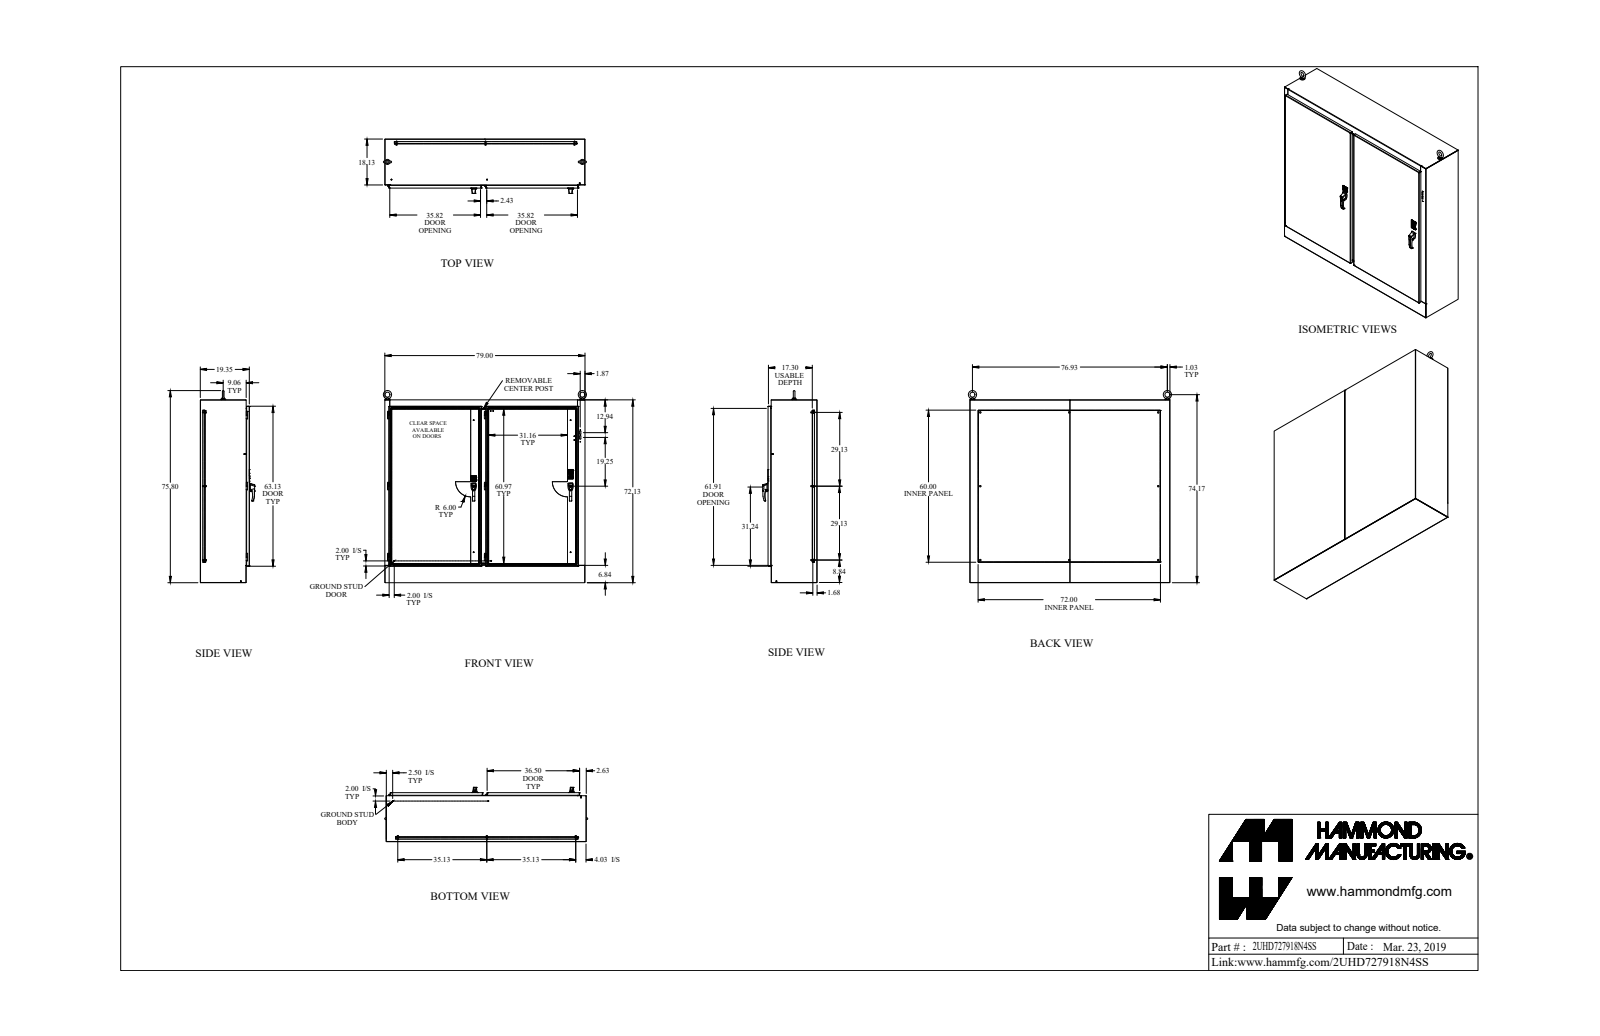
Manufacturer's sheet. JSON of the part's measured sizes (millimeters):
{"part_name": "2UHD727918N4SS", "step_written_by": "SolidWorks 2018 (AUTOMOTIVE_DESIGN)", "units": "millimeters", "bodies": {"solids": 222, "faces": 3298, "planar": 1929, "cylindrical": 982, "other": 387}, "overall_size": [2036.6, 1925.3, 545.2], "volume_mm3": 70730000, "surface_area_mm2": 32550000, "round_holes": [[6.4, 14], [5, 13], [7.1, 9], [7.8, 9], [8.9, 8], [6.5, 6], [6.5, 6], [8, 6], [5.1, 5], [8, 5], [11.3, 5], [4, 4]], "round_bosses_or_shafts": [[6.4, 18], [25.4, 14], [16.5, 9], [9.5, 8], [8.4, 8], [19.1, 6], [15.9, 6], [12.7, 6]], "partial_cylinders_radius": [[3.2, 67], [12.7, 38], [1.2, 34], [3.6, 34], [0.4, 32], [1.5, 29], [0.8, 28], [6.4, 26]], "face_to_face_distances": [2.4, 1.8, 443.5, 491.9, 489.5, 48.4, 46, 44.2, 46.6, 445.3], "hole_center_spacings": [971.6, 25.4, 32.7, 43.7, 87.1, 633.4, 690.6, 972]}
